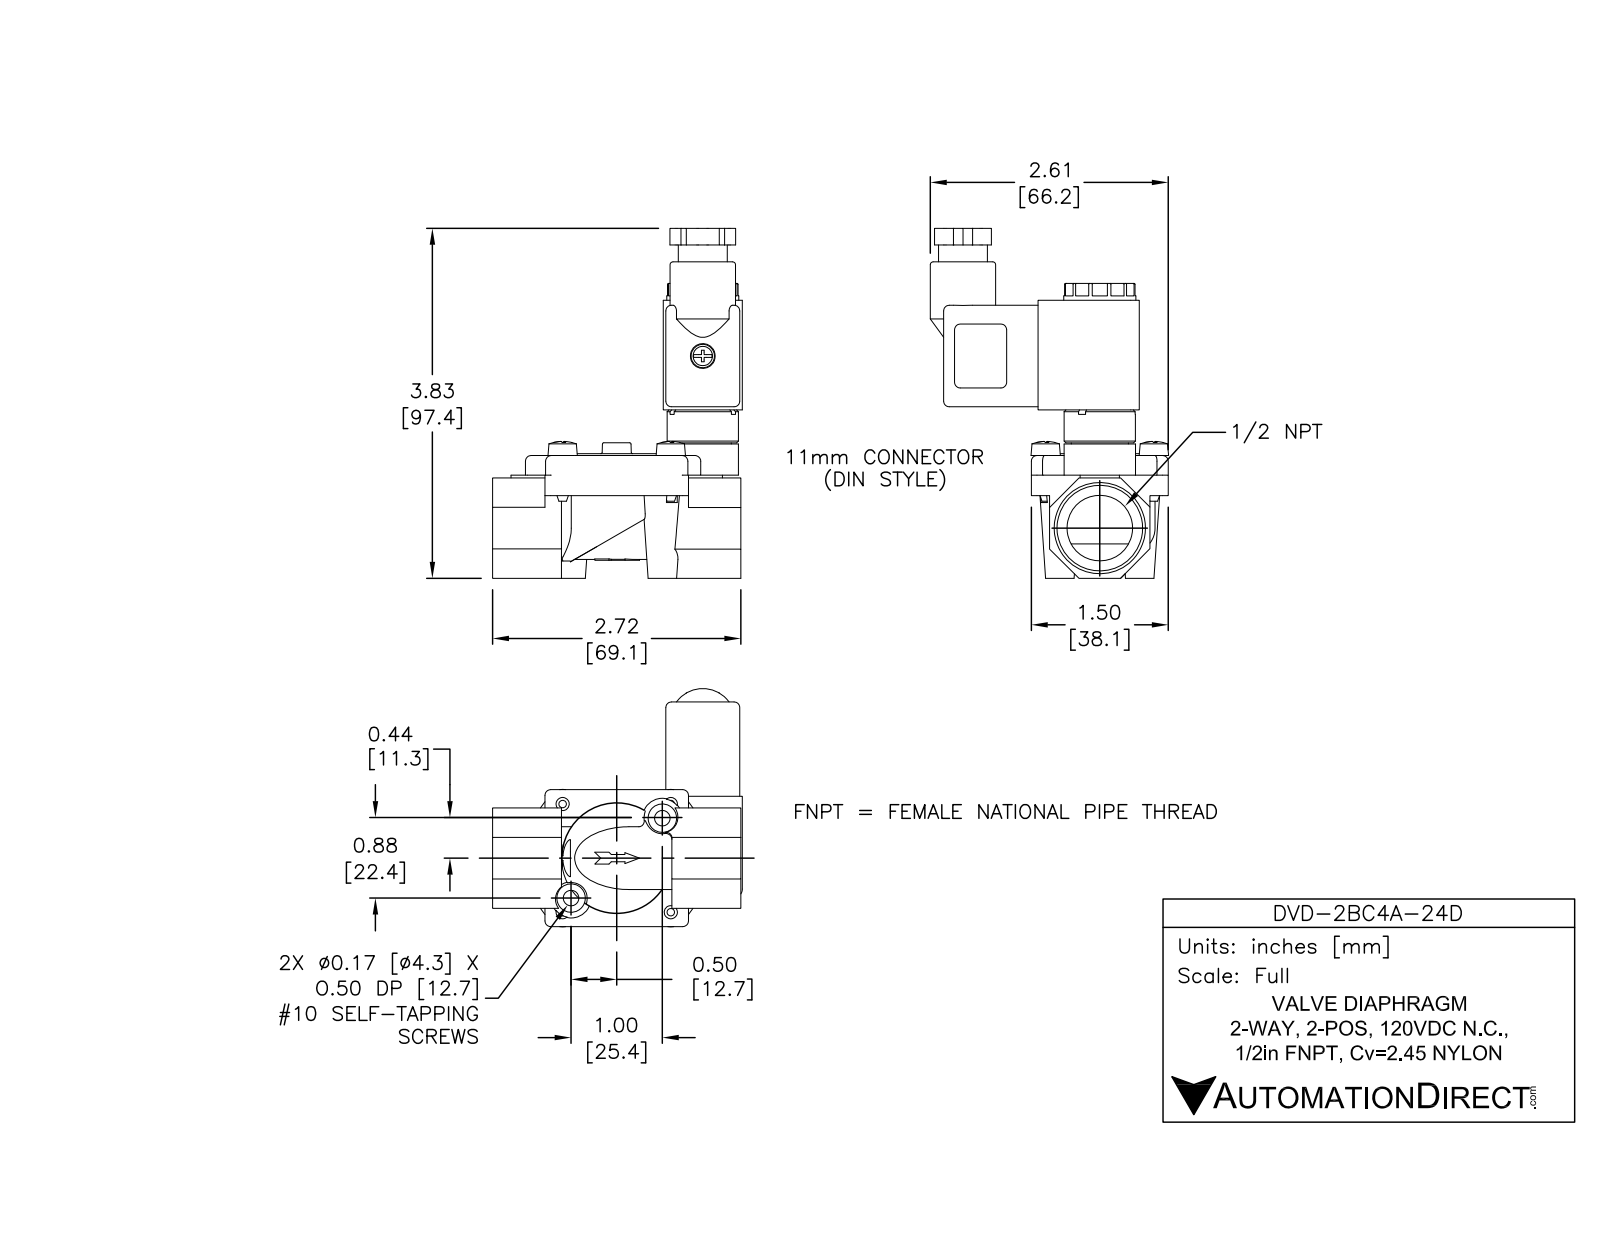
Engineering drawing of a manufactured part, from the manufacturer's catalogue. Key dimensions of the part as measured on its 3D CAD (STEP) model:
Part name (STEP PRODUCT): DVD-2BC4A-24D
STEP written by: SolidWorks 2015 (AUTOMOTIVE_DESIGN)
Units: inches
Bodies: 13 solids, 1449 faces (725 planar, 257 cylindrical, 467 other)
Overall size (bounding box): 3.834 × 2.736 × 2.611
Volume: 3.855 in³ · Surface area: 61.59 in²
Round holes (diameter × count): ⌀0.144 ×4, ⌀0.164 ×4, ⌀0.06 ×2, ⌀0.093 ×2, ⌀0.17 ×2, ⌀0.703 ×2, ⌀0.062 ×1, ⌀0.156 ×1, ⌀0.166 ×1, ⌀0.25 ×1, ⌀0.272 ×1, ⌀0.312 ×1
Round bosses / shafts (diameter × count): ⌀0.187 ×4, ⌀0.125 ×4, ⌀0.625 ×2, ⌀1.375 ×1, ⌀0.79 ×1, ⌀0.782 ×1, ⌀0.781 ×1, ⌀0.716 ×1
Partial cylindrical surfaces — rounded edges, fillets, slot ends (radius × count): R0.01 ×24, R0.062 ×24, R0.156 ×12, R0.044 ×3, R0.094 ×2, R0.215 ×2, R0.314 ×1, R0.344 ×1
Main face-to-face distances: 0.05, 1.1, 0.866, 0.76, 0.2, 1.3, 0.788, 0.078, 0.078, 0.71
Hole centre spacings: 0.838, 1.185, 0.181, 0.664, 0.688, 1.034, 1.104, 1.502
